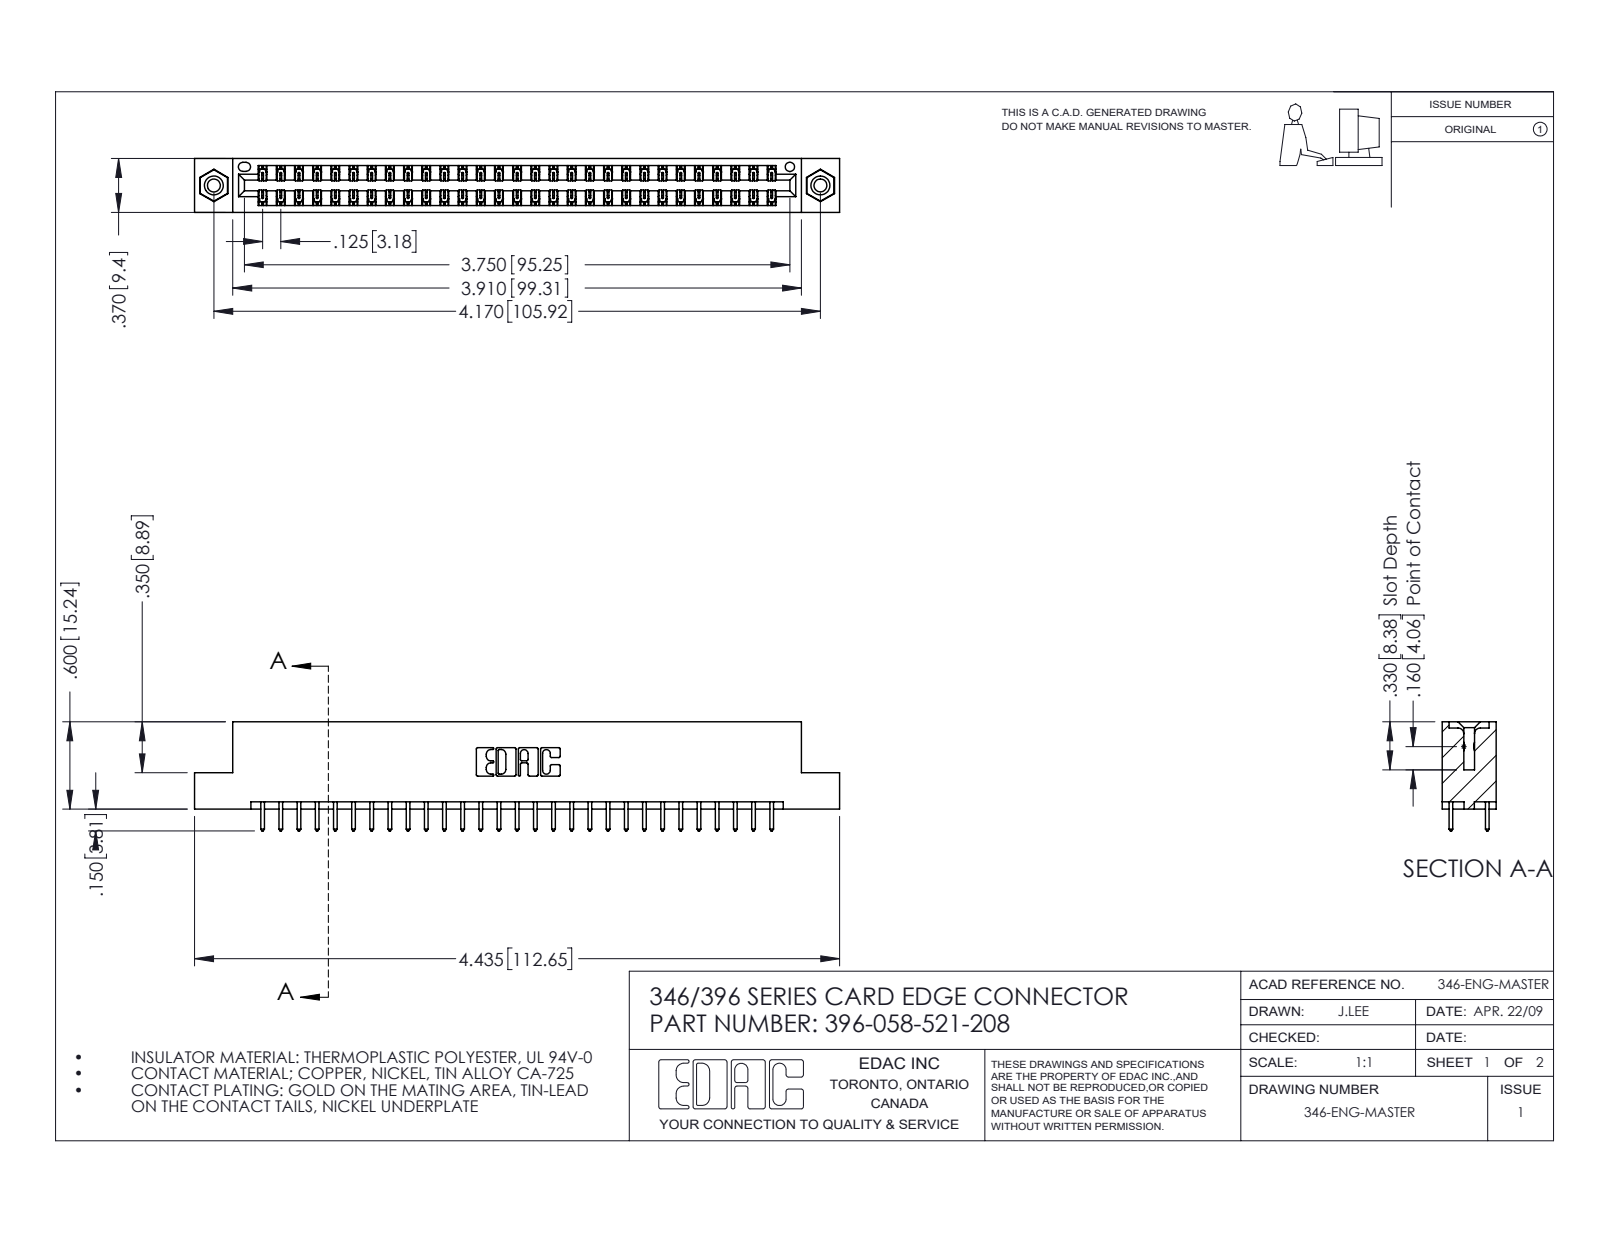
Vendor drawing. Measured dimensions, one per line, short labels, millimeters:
name: 345-250-001_345-250-003-102; 396-058-521-208; 346 Part_Flush Mounting Lugs - 0.156 Dia-TI; 345-292-001_345-293-121
written by: SolidWorks 2016 (CONFIG_CONTROL_DESIGN)
unit: mm
bodies: 61 solids, 3198 faces (2138 planar, 1044 cylindrical, 16 other)
size: 112.6 × 19.1 × 9.4
volume: 10 800 mm³; area: 14 570 mm²
holes: 2× ⌀2.3, 2× ⌀3.2, 2× ⌀4, 1× ⌀1.6
bosses: 2× ⌀3.9
rounds: 87× R0.2, 58× R0.3, 22× R0.3, 6× R0.2, 6× R0.8, 3× R0.7, 2× R0.4, 2× R0.6
face distances: 1.2, 8.2, 6.4, 9.4, 1.8, 7.6, 0.6, 7, 3.8, 5.6
hole spacings: 6.2, 100.6, 105.9
